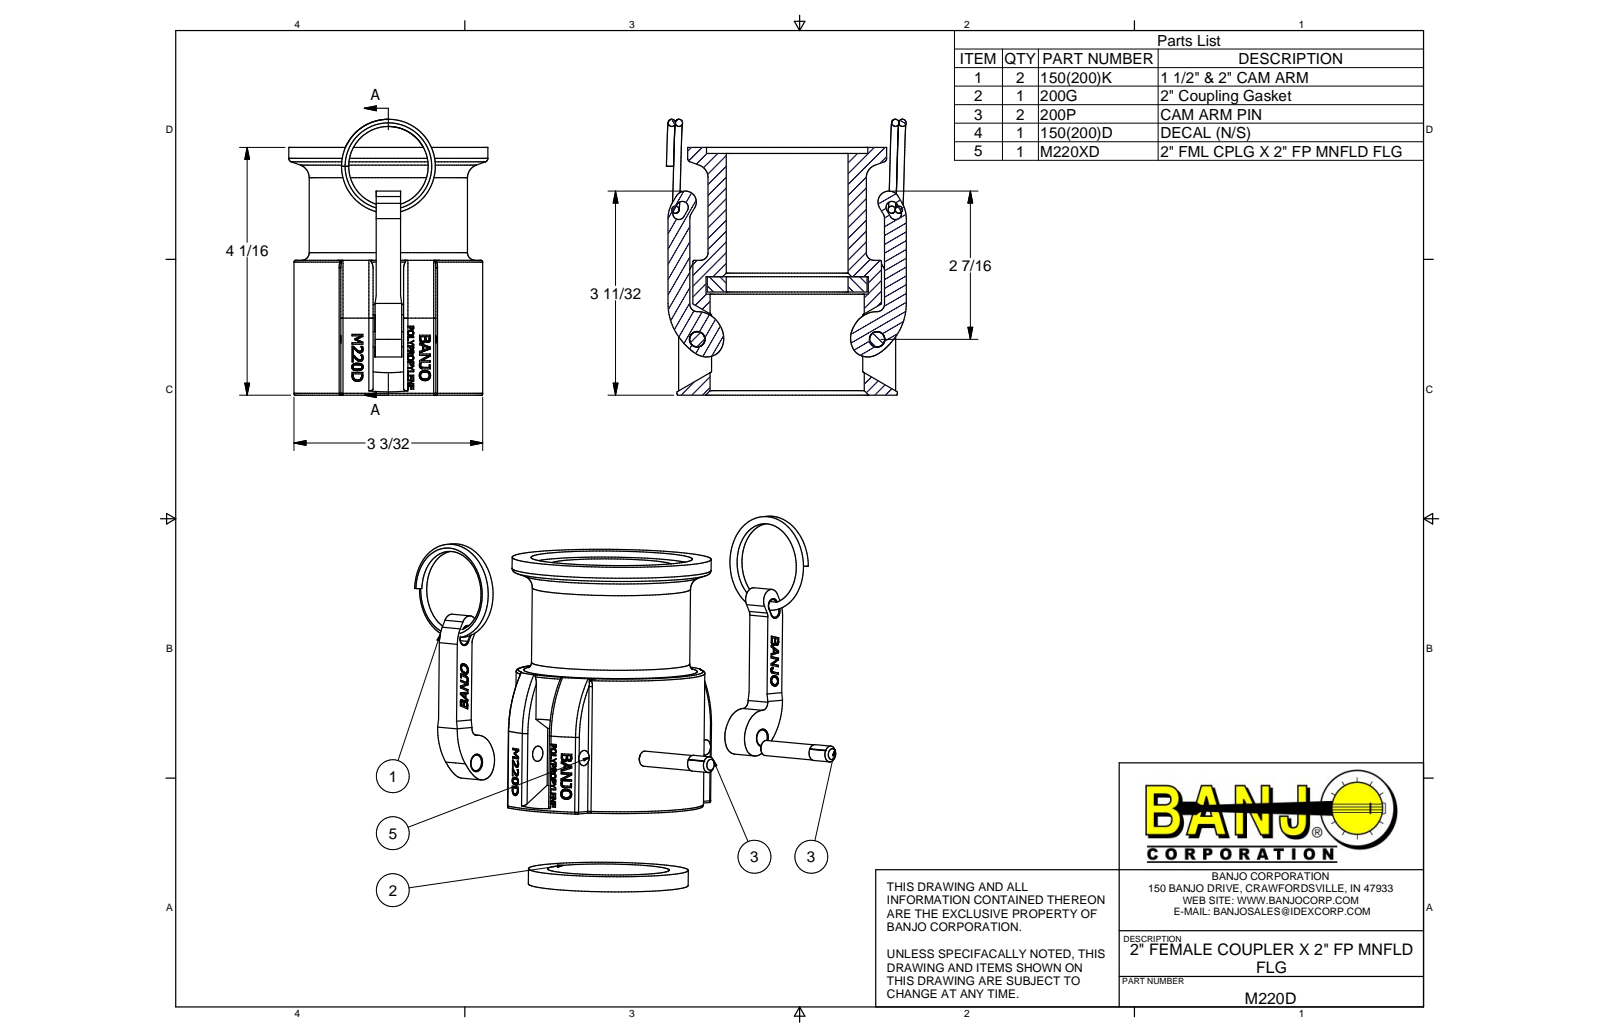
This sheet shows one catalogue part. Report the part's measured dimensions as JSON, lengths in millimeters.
{"part_name": "M220XD; 150(200)XK; 150RING; 150(200)K (+3 more)", "step_written_by": "Autodesk Inventor 2014 (AUTOMOTIVE_DESIGN)", "units": "millimeters", "bodies": {"solids": 8, "faces": 857, "planar": 408, "cylindrical": 95, "other": 354}, "overall_size": [114.83, 100.76, 83.06], "volume_mm3": 214128, "surface_area_mm2": 73325, "round_holes": [[6.35, 2], [6.55, 2], [50.8, 1], [64.31, 1], [67.31, 1], [67.69, 1]], "round_bosses_or_shafts": [[6.6, 2], [6.32, 2], [83.06, 1], [66.67, 1], [66.04, 1]], "partial_cylinders_radius": [[1.52, 14], [2.48, 4], [3.15, 2], [3.17, 2], [4.55, 2], [12.7, 2], [23.88, 2], [39.37, 1]], "face_to_face_distances": [53.85, 103.12, 49.27, 2.54, 51.31, 100.58, 60.2, 57.66, 6.35, 42.92], "hole_center_spacings": [75.06]}
